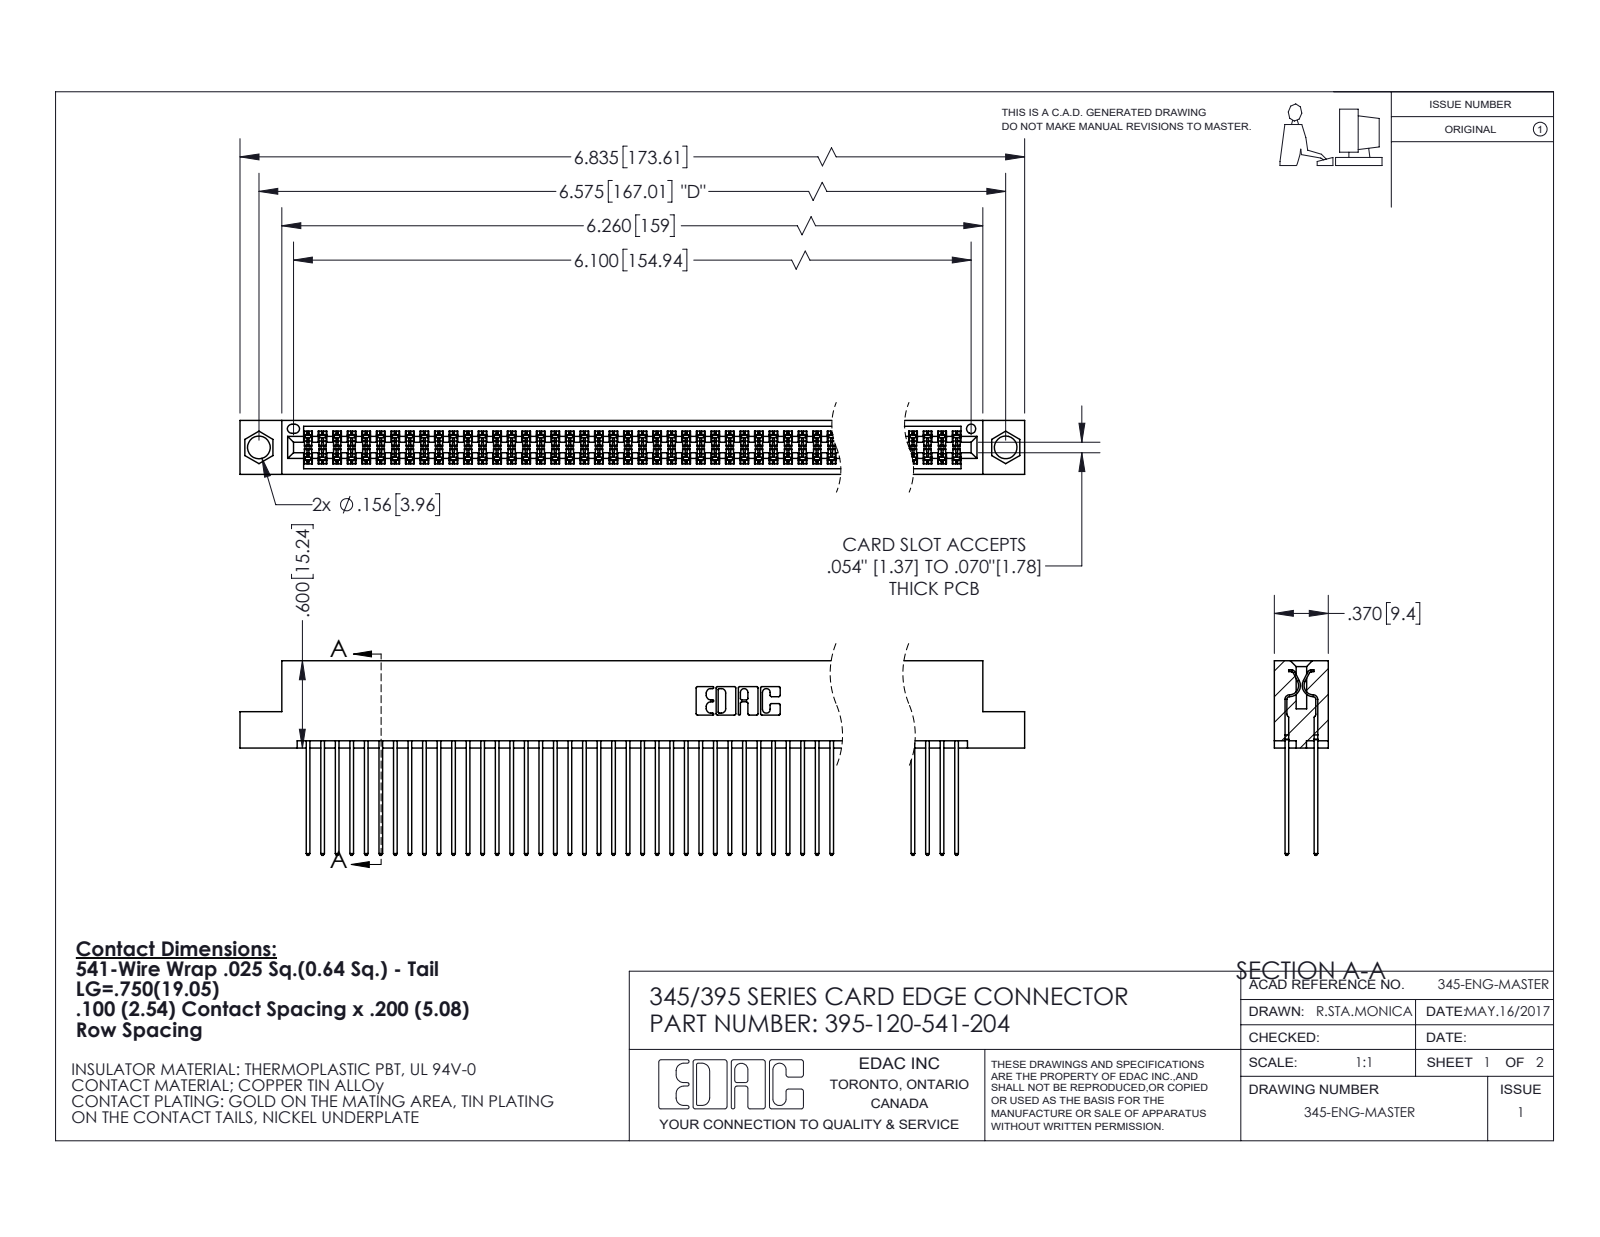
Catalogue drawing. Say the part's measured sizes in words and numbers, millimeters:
The part is named "345 Part_Flush Mounting Lugs - 0.156 Dia-TI; 395-120-541-204; 345-292-001_345-293-141". Its 3-D file was written by "SolidWorks 2020 (CONFIG_CONTROL_DESIGN)". It is 121 solids with 6140 faces: 4054 planar, 2086 cylindrical and 0 other. Overall it measures 173.6 by 34 by 9.4 millimeters. Its volume is 17 620 cubic millimeters and its surface area 29 470 square millimeters. Round holes: 2 of diameter 4, 1 of diameter 1.6. Partial cylindrical surfaces (rounded edges, fillets, slot ends): 180 of radius 0.2, 120 of radius 0.3, 22 of radius 0.3, 6 of radius 0.2, 6 of radius 0.8, 3 of radius 0.7, 2 of radius 0.4, 2 of radius 0.5. The main face-to-face distances are 7.6, 1.8, 5.1, 2.5, 6.9, 0.6, 5.7, 9.4, 4.4, 3.8. The hole center spacings are 6.9, 161, 167.
